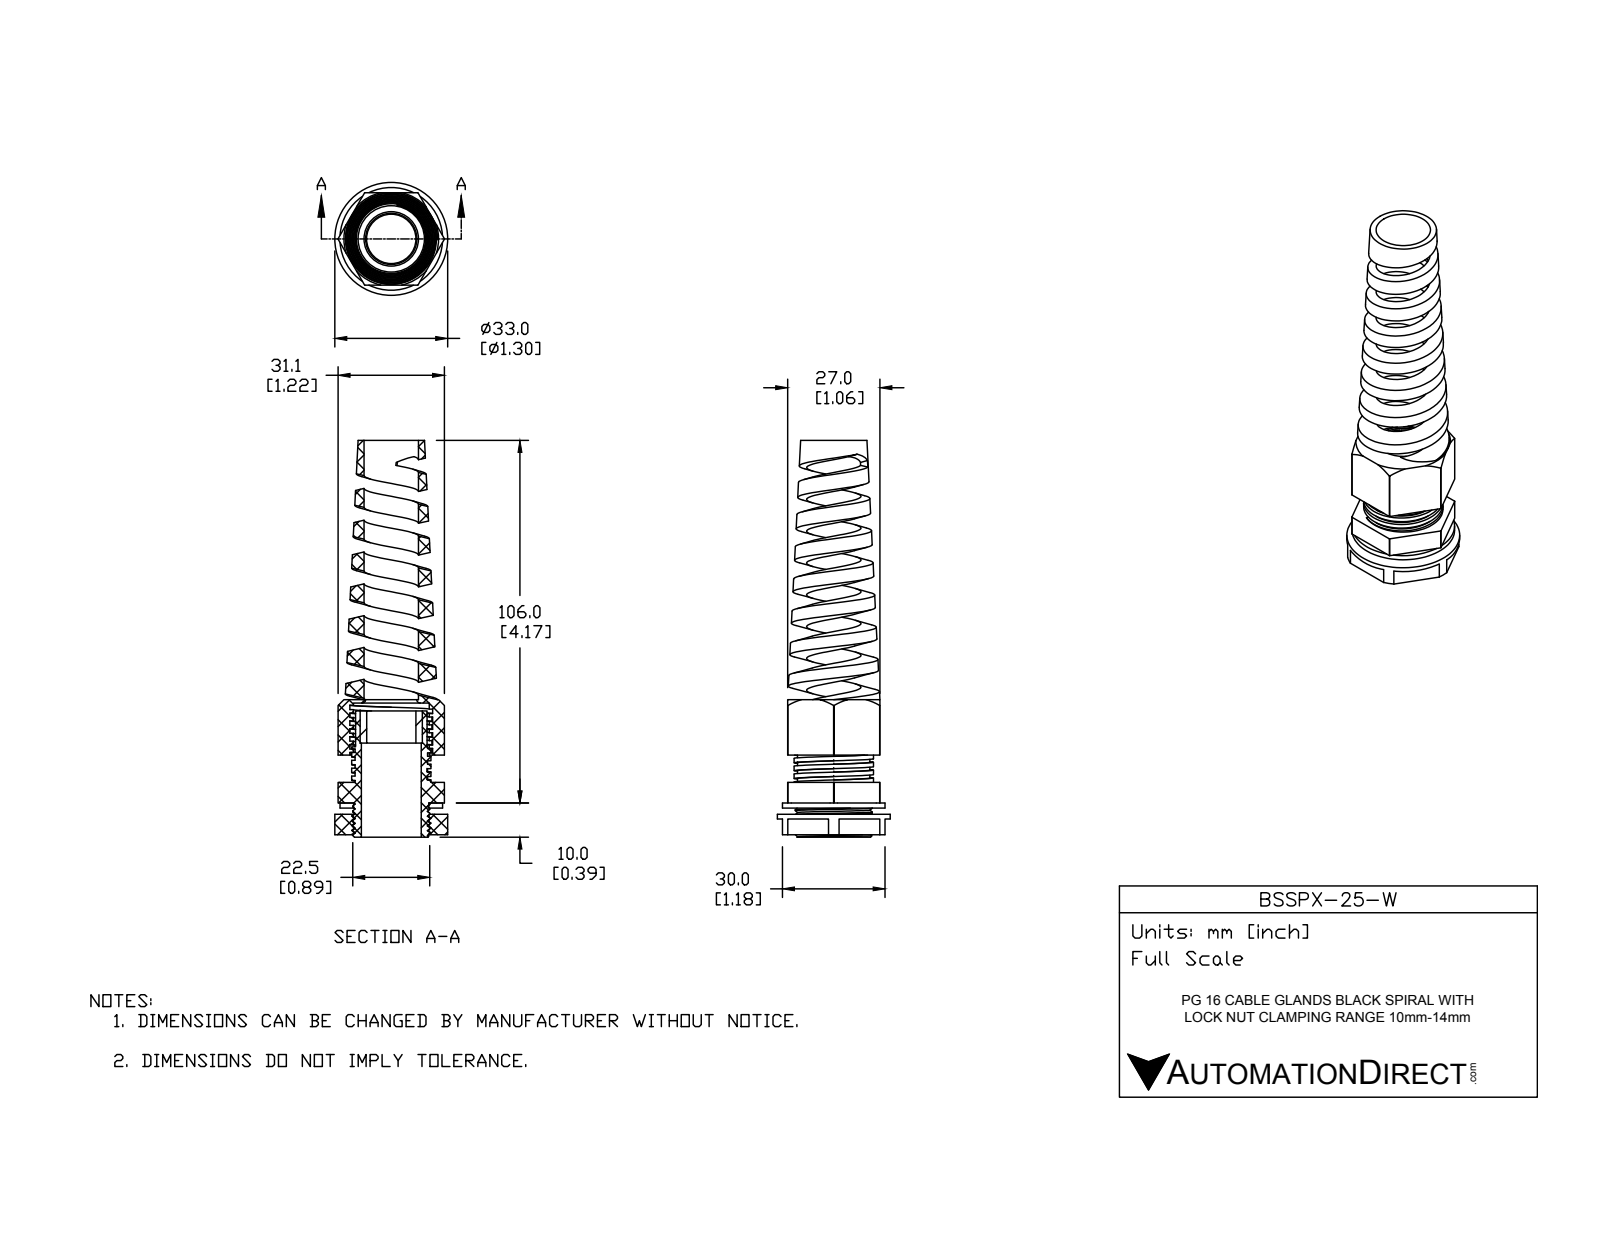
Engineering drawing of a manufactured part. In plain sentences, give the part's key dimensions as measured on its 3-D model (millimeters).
The part is named "BSSPX-25-W". Its 3-D file was written by "SolidWorks 2015 (CONFIG_CONTROL_DESIGN)". It is 5 solids with 240 faces: 103 planar, 96 cylindrical and 41 other. Overall it measures 116 by 33 by 33 millimeters. Its volume is 22 193 cubic millimeters and its surface area 23 707 square millimeters. Round holes: 1 of diameter 14.4, 1 of diameter 15.9, 1 of diameter 17.5, 1 of diameter 18.2, 1 of diameter 21.83, 1 of diameter 22, 1 of diameter 22.2. Round bosses or shafts: 1 of diameter 33, 1 of diameter 30, 1 of diameter 23.2, 1 of diameter 22.5, 1 of diameter 20.91. Partial cylindrical surfaces (rounded edges, fillets, slot ends): 1 of radius 15.55. The main face-to-face distances are 27, 1.5, 8.5, 6, 1, 2.5, 31.7, 28.5, 7.5, 7.
